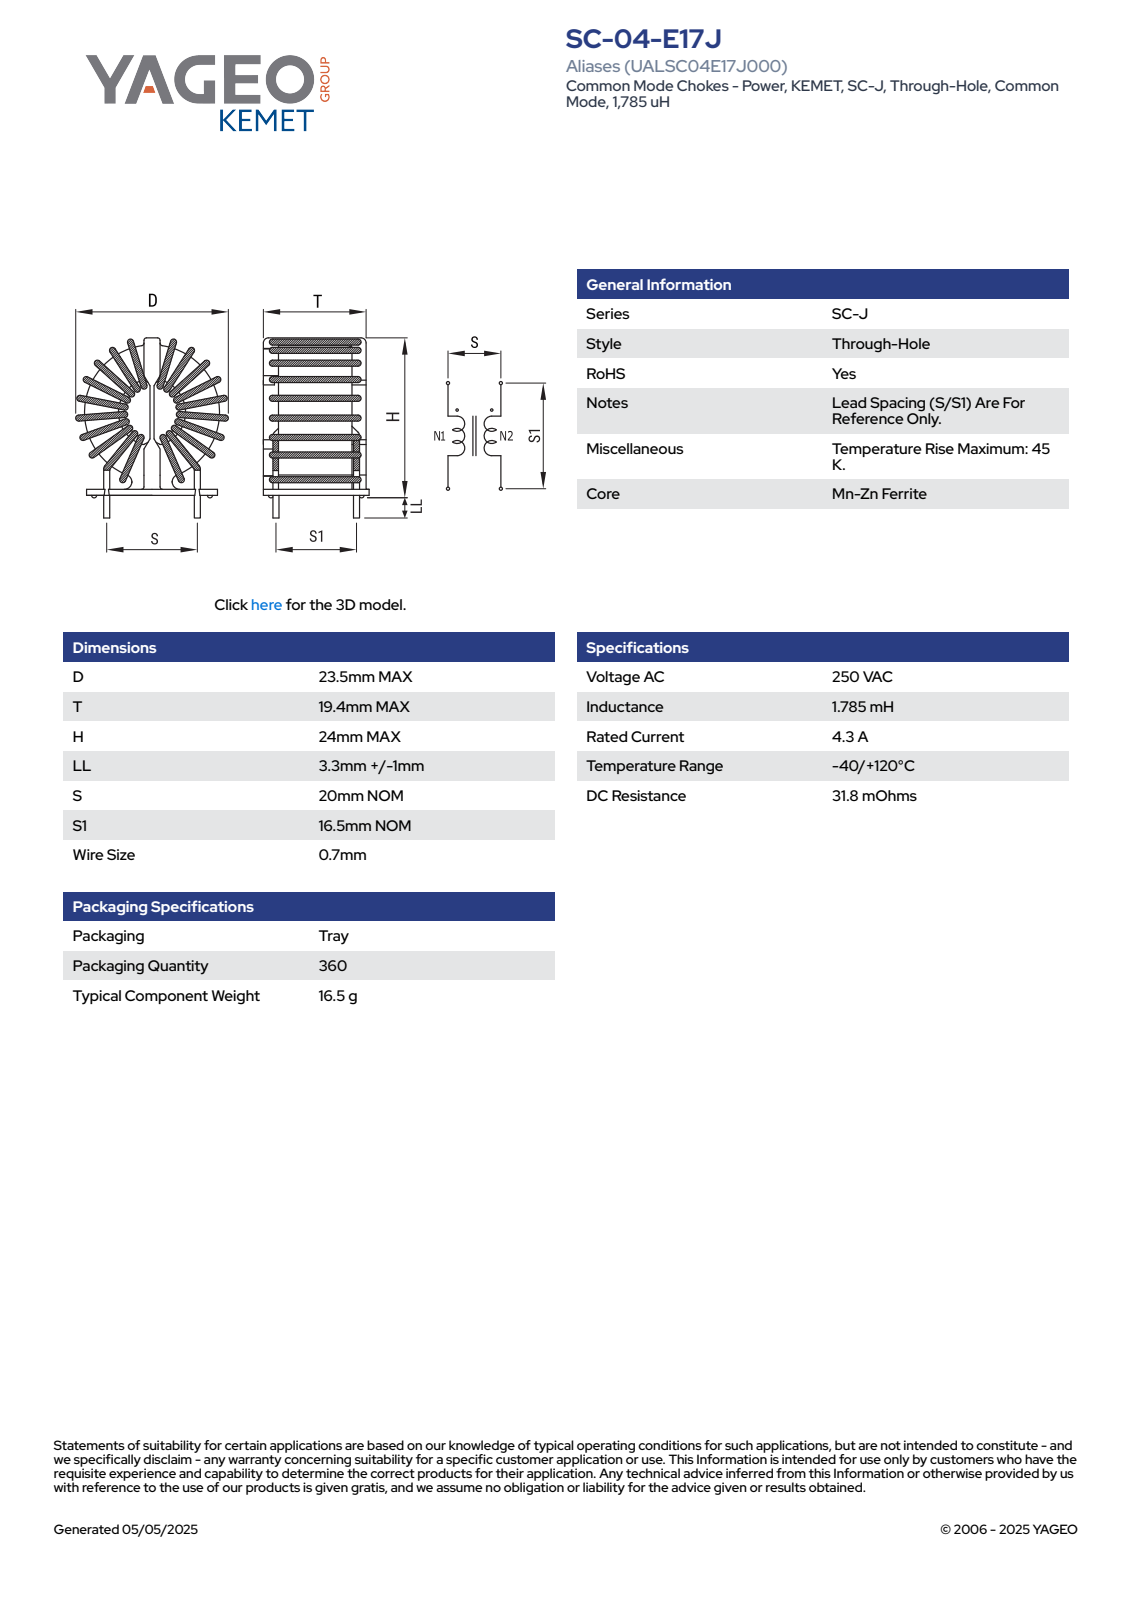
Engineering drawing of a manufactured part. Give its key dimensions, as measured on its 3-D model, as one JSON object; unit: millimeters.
{"part_name": "SC-04-E17J", "step_written_by": "SolidWorks 2018 (AUTOMOTIVE_DESIGN)", "units": "millimeters", "bodies": {"solids": 1, "faces": 314, "planar": 143, "cylindrical": 109, "other": 62}, "overall_size": [27.3, 23.5, 19.4], "volume_mm3": 6185, "surface_area_mm2": 4821, "round_bosses_or_shafts": [[0.7, 8]], "partial_cylinders_radius": [[0.35, 18], [0.2, 8], [0.42, 4], [1, 4], [3, 1], [4.2, 1], [4.7, 1], [4.78, 1]], "face_to_face_distances": [2, 0.7, 16, 0.5, 13.35, 1.2, 3.58, 2.5, 3.2, 0.93]}
